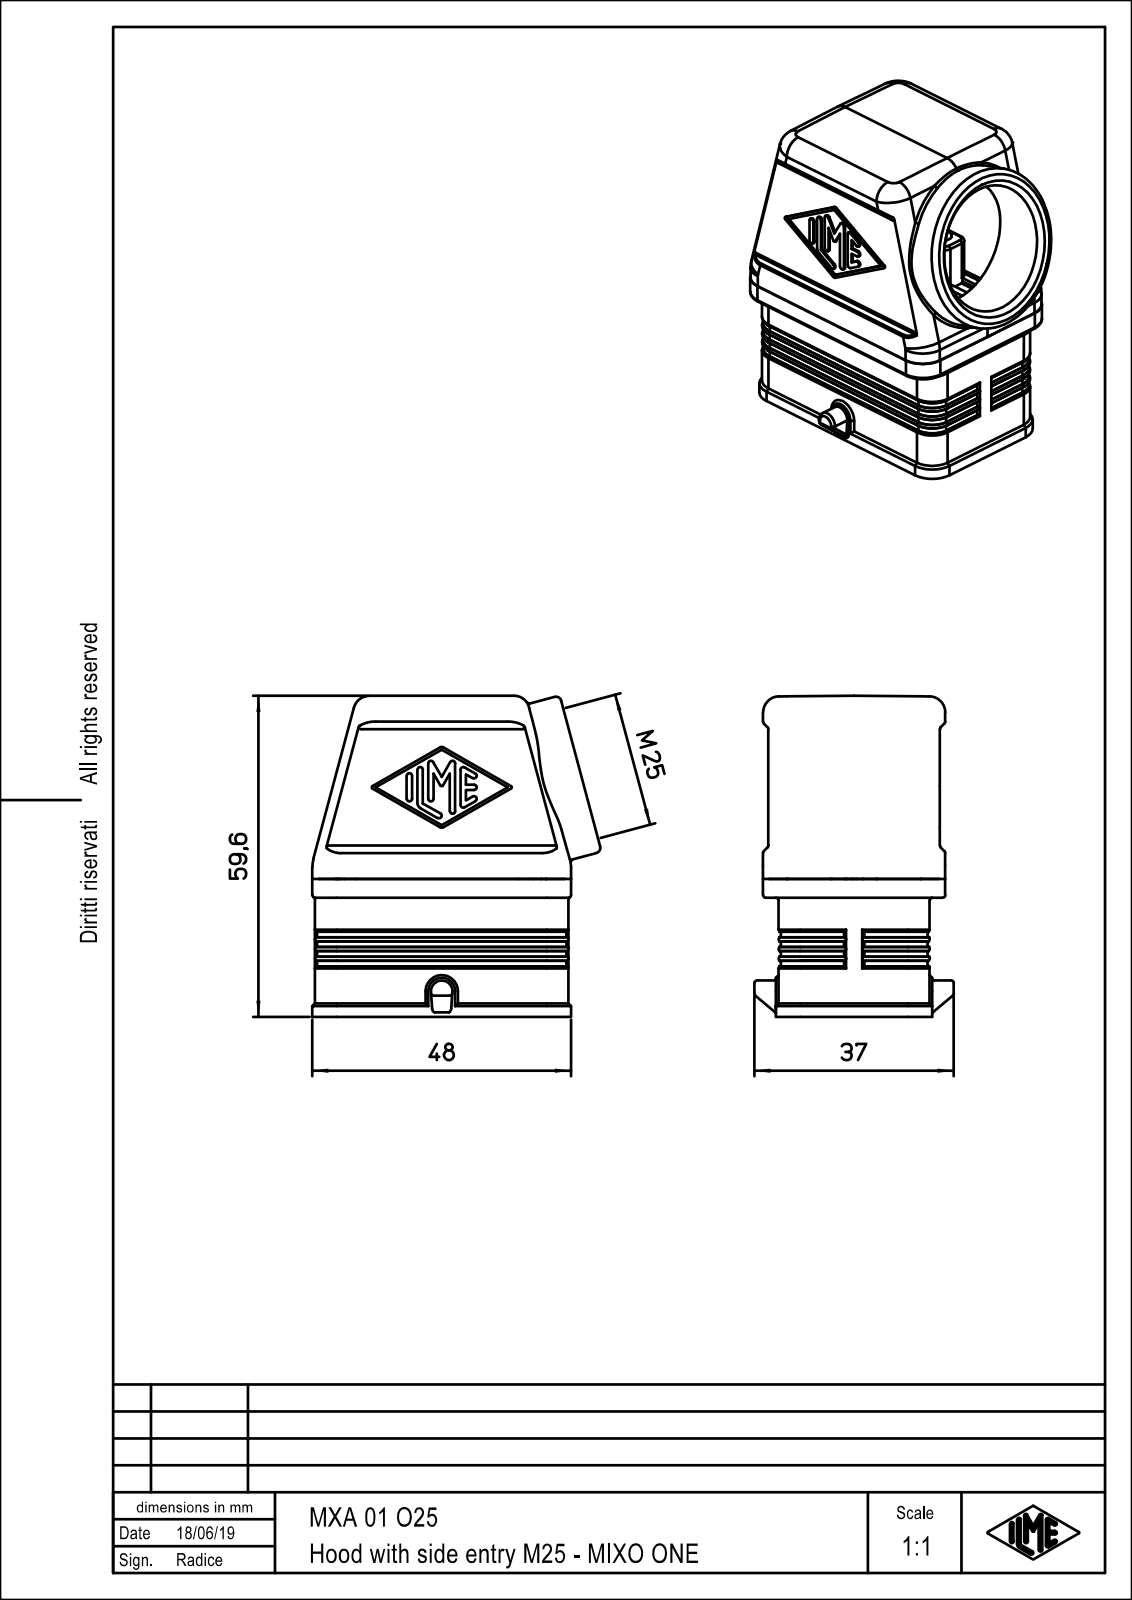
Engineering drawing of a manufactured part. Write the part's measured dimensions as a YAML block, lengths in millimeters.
part_name: "MXA_01_O25"
step_written_by: "Creo Elements/Direct Modeling 20.1B 02-Apr-2019 (C) Parametric Technology GmbH (AUTOMOTIVE_DESIGN)"
units: millimeters
bodies: {solids: 1, faces: 680, planar: 385, cylindrical: 177, other: 118}
overall_size: [60, 53.43, 37]
volume: 24835
surface_area: 25159
round_holes:
  - {diameter: 25, count: 1}
round_bosses_or_shafts:
  - {diameter: 5.5, count: 2}
  - {diameter: 30, count: 1}
  - {diameter: 5, count: 1}
  - {diameter: 4, count: 1}
  - {diameter: 2, count: 1}
partial_cylinders:
  - {radius: 0.5, count: 41}
  - {radius: 1, count: 23}
  - {radius: 4.5, count: 20}
  - {radius: 0.7, count: 16}
  - {radius: 3, count: 6}
  - {radius: 2.35, count: 4}
  - {radius: 2.8, count: 4}
  - {radius: 3.4, count: 4}
face_to_face_distances: [1.5, 30.3, 28.8, 1, 1.7, 0.4, 3.6, 2.1, 26.7, 28.2]
